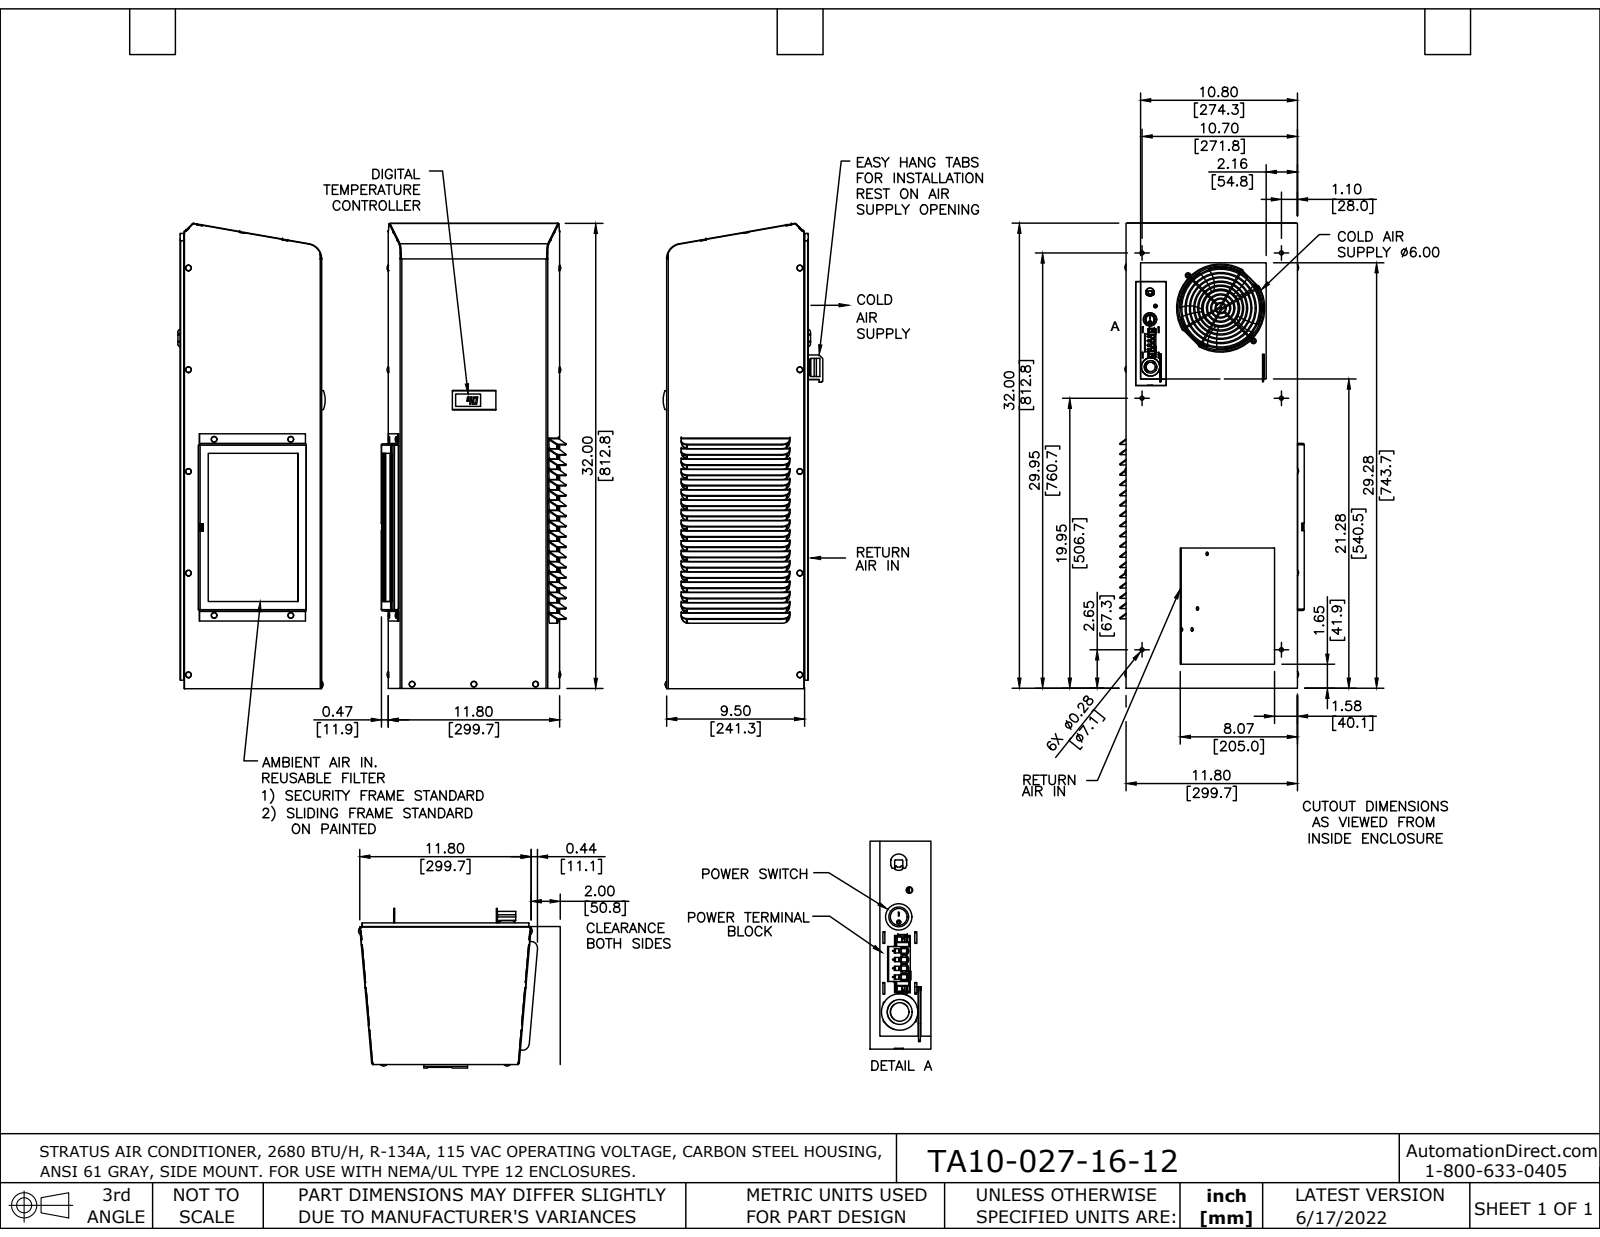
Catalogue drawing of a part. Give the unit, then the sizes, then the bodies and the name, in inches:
Units: inches
Overall size (bounding box): 32.024 × 12.576 × 11.549
Round holes (diameter × count): ⌀0.159 ×11, ⌀0.204 ×5, ⌀1.236 ×1, ⌀1.816 ×1, ⌀2.406 ×1, ⌀3.016 ×1, ⌀3.566 ×1, ⌀4.156 ×1, ⌀4.756 ×1, ⌀5.356 ×1, ⌀5.779 ×1, ⌀6 ×1
Round bosses / shafts (diameter × count): ⌀0.19 ×7, ⌀0.248 ×2, ⌀6.07 ×1, ⌀5.996 ×1, ⌀5.5 ×1, ⌀4.9 ×1, ⌀4.3 ×1, ⌀3.71 ×1
Partial cylindrical surfaces — rounded edges, fillets, slot ends (radius × count): R0.015 ×45, R0.01 ×42, R0.5 ×36, R0.506 ×36, R0.1 ×28, R0.058 ×21, R0.116 ×21, R0.031 ×12
Main face-to-face distances: 0.058, 9.435, 0.058, 9.377, 9.493, 0.09, 0.16, 0.25, 0.102, 9.275
Hole centre spacings: 7, 14, 21, 1.732, 5.3, 6.565, 12.12, 13.228
Volume: 148 in³ · Surface area: 3 233 in²
Bodies: 3 solids, 1686 faces (1062 planar, 535 cylindrical, 89 other)
Part name (STEP PRODUCT): TA10-027-16-12
STEP written by: SolidWorks 2021 (AUTOMOTIVE_DESIGN)
